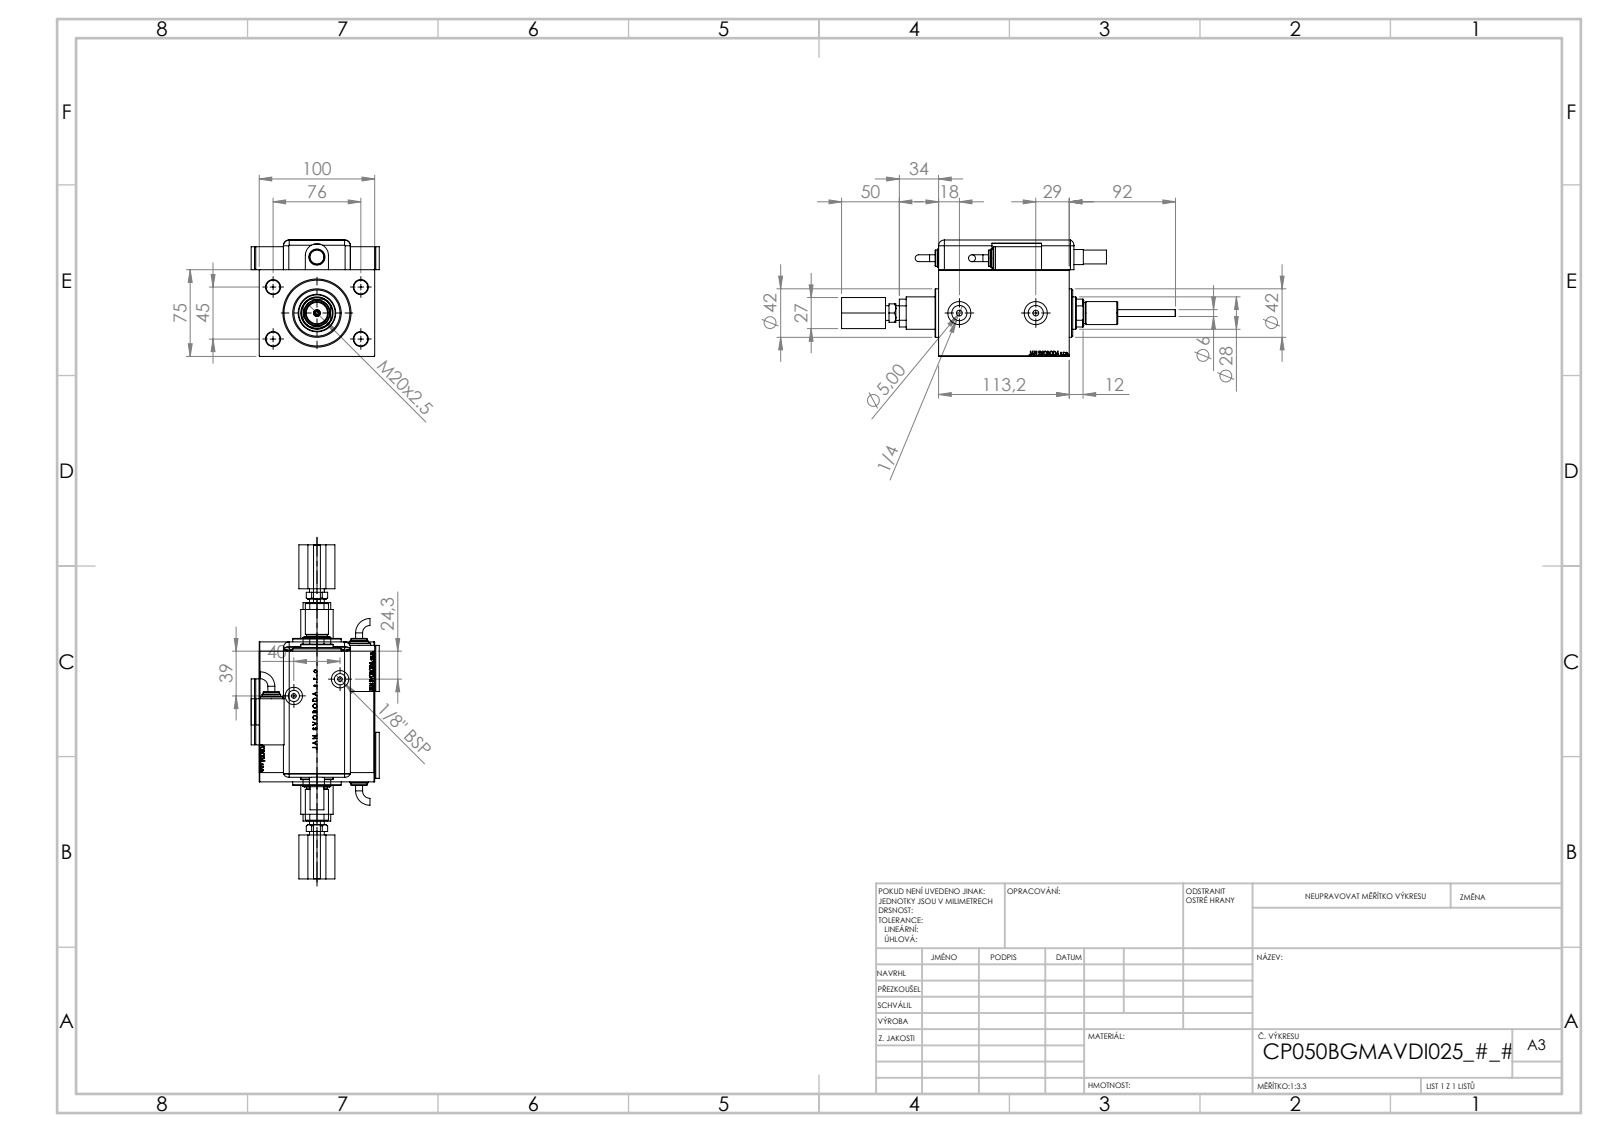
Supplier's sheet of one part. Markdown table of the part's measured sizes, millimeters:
| quantity | value |
| --- | --- |
| part name | V450DCP_B_VCP; TYC; V450CP_MALE_METRIC; V450DCP_VC_B (+6 more) |
| STEP written by | SolidWorks 2019 (CONFIG_CONTROL_DESIGN) |
| units | millimeters |
| bodies | 11 solids, 1322 faces (618 planar, 141 cylindrical, 563 other) |
| overall size | 289.2 × 111 × 100.8 |
| volume | 981 971 mm³ |
| surface area | 182 699 mm² |
| round holes (diameter × count) | 4 × 4, 12 × 4, 5 × 2, 8 × 2, 9.73 × 2, 13.16 × 2, 15 × 2, 20 × 2, 3 × 1, 6 × 1, 14 × 1, 18.5 × 1 |
| round bosses / shafts (diameter × count) | 20 × 3, 16 × 2, 14 × 2, 6 × 2, 42 × 1, 18 × 1, 13 × 1, 12.78 × 1 |
| partial cylindrical surfaces (radius × count) | 5 × 9, 10 × 1, 13.5 × 1 |
| main face-to-face distances | 3, 75, 100, 113.2, 1, 100.8, 25.8, 14, 99.2, 24 |
| hole center spacings | 44.16, 45, 46.04, 76, 80.53, 88.32, 20, 20.42 |
